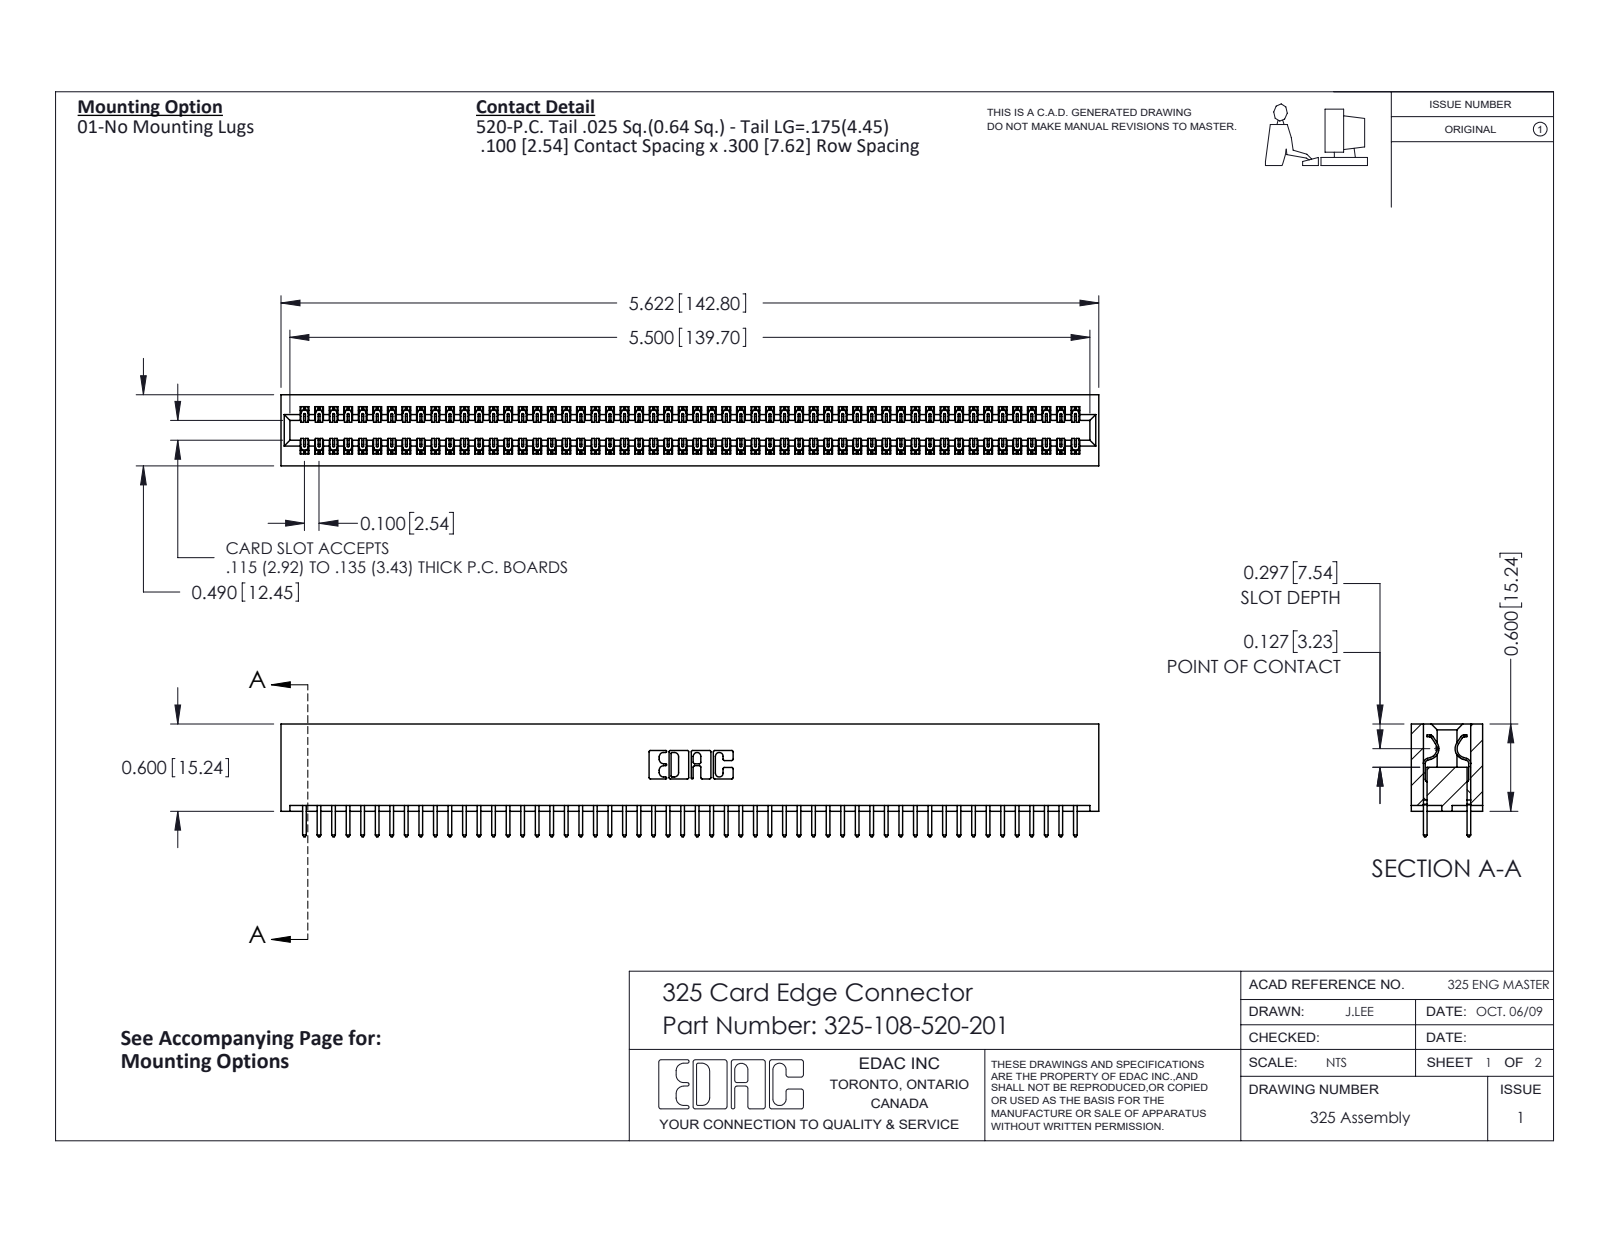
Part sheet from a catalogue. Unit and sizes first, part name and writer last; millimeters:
Units: millimetres
Overall size (bounding box): 142.8 × 19.7 × 12.4
Partial cylindrical surfaces — rounded edges, fillets, slot ends (radius × count): R0.2 ×162, R0.3 ×108, R0.3 ×22, R0.2 ×6, R0.8 ×6, R0.7 ×3, R0.4 ×2, R0.6 ×2
Main face-to-face distances: 2.1, 10.3, 7.6, 12.4, 2.7, 9.7, 0.6, 8.3, 7, 14.2
Volume: 19 140 mm³ · Surface area: 23 880 mm²
Bodies: 109 solids, 5722 faces (3954 planar, 1768 cylindrical, 0 other)
Part name (STEP PRODUCT): 325-108-520-201; 325-292-001_325-293-120; 325 Part_Lugless
STEP written by: SolidWorks 2016 (CONFIG_CONTROL_DESIGN)
